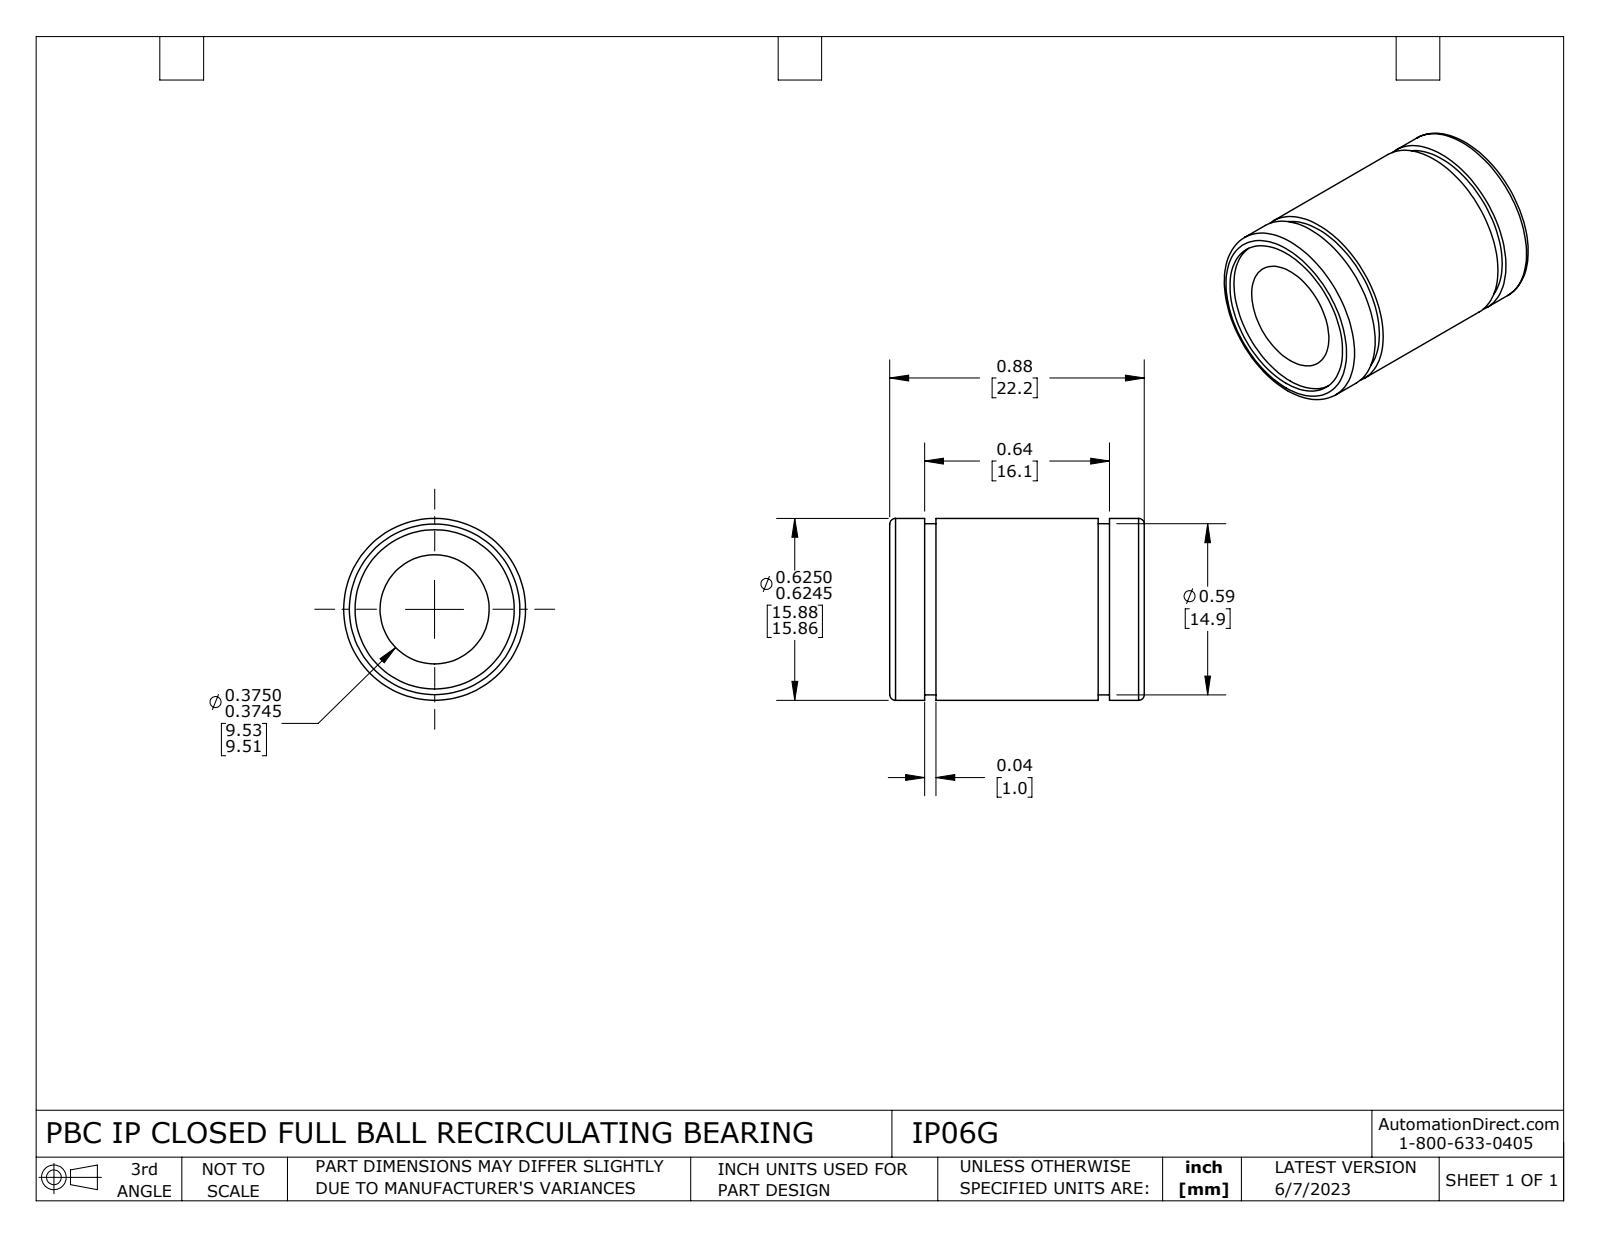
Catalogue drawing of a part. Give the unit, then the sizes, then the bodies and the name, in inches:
Units: inches
Overall size (bounding box): 0.875 × 0.625 × 0.625
Round holes (diameter × count): ⌀0.375 ×1, ⌀0.547 ×1
Round bosses / shafts (diameter × count): ⌀0.625 ×1, ⌀0.588 ×1
Main face-to-face distances: 0.836, 0.1, 0.139, 0.697, 0.736, 0.039, 0.596, 0.019, 0.12, 0.159
Volume: 0.164 in³ · Surface area: 3.261 in²
Bodies: 1 solid, 28 faces (8 planar, 16 cylindrical, 4 other)
Part name (STEP PRODUCT): IP06G
STEP written by: SolidWorks 2021 (CONFIG_CONTROL_DESIGN)
